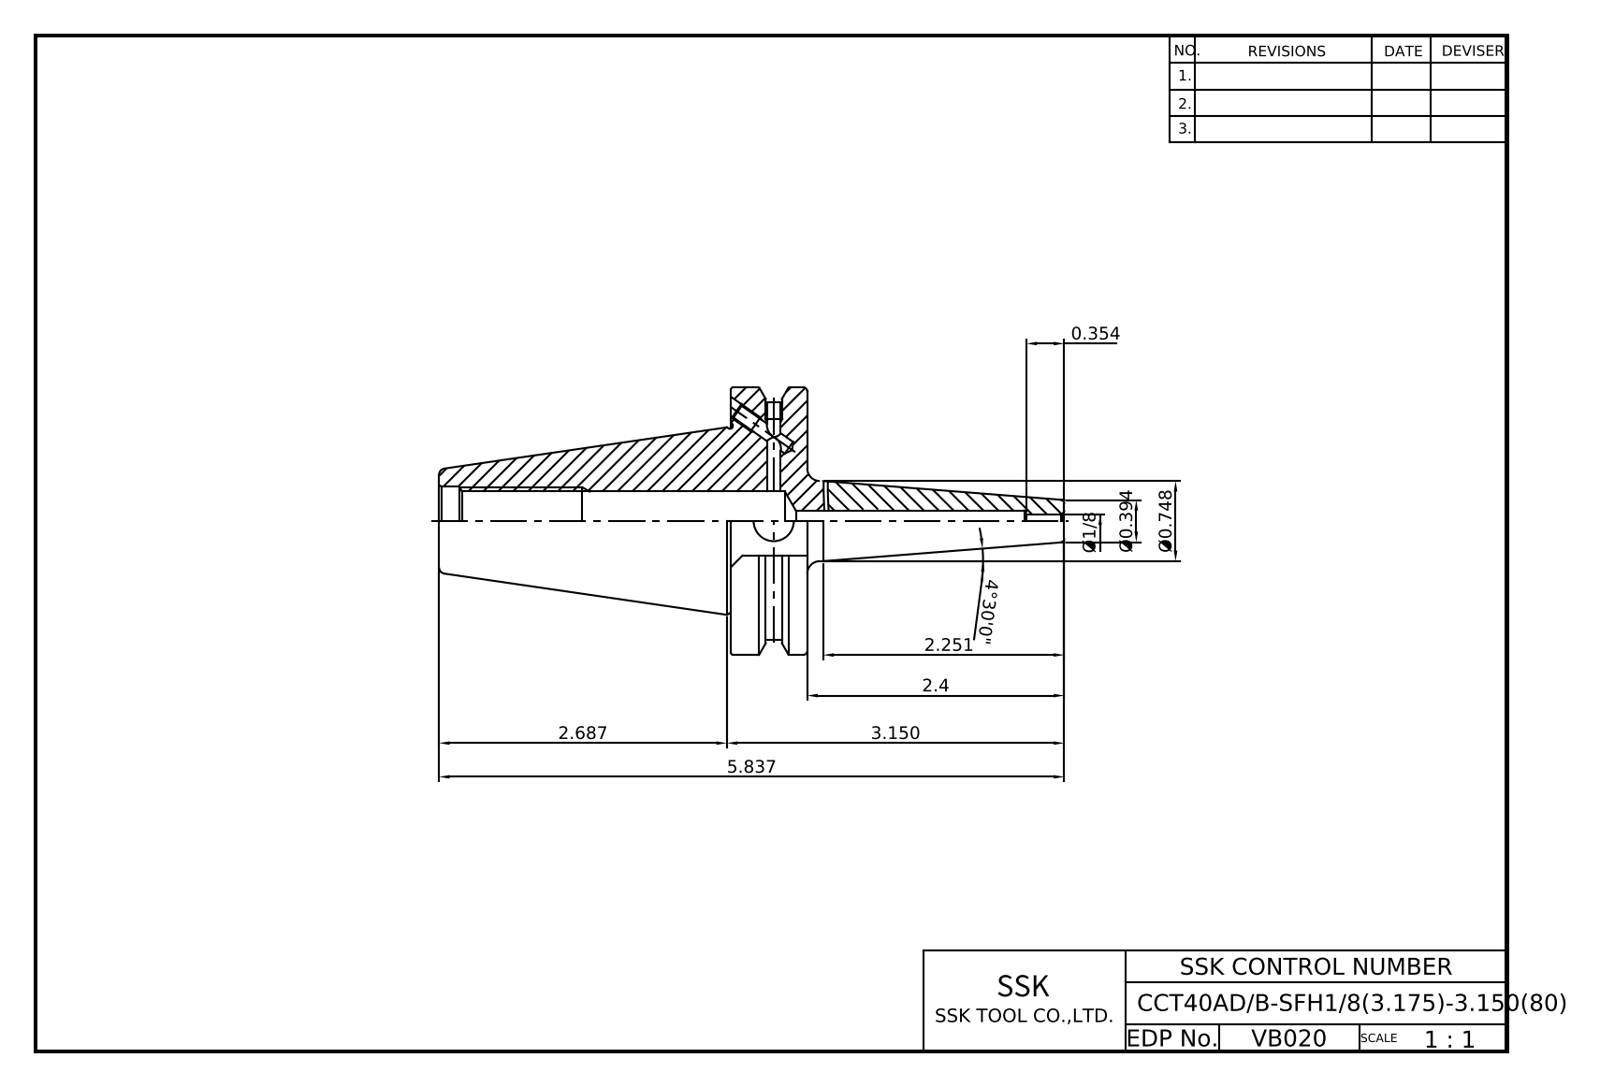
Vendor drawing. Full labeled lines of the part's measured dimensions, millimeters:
Part name (STEP PRODUCT): LO CCT40ADB-SFH3.175-3.15
STEP written by: Autodesk Inventor 2022 (AUTOMOTIVE_DESIGN)
Units: millimetres
Bodies: 1 solid, 88 faces (36 planar, 28 cylindrical, 24 other)
Overall size (bounding box): 148.25 × 63.5 × 61.09
Volume: 113 513 mm³ · Surface area: 24 719 mm²
Round holes (diameter × count): ⌀3.24 ×4, ⌀4 ×2, ⌀4.2 ×2, ⌀3.17 ×1, ⌀5 ×1, ⌀9.53 ×1, ⌀13 ×1, ⌀13.39 ×1, ⌀16.3 ×1
Round bosses / shafts (diameter × count): ⌀63.5 ×1, ⌀43.8 ×1, ⌀19 ×1
Partial cylindrical surfaces — rounded edges, fillets, slot ends (radius × count): R28.15 ×1
Main face-to-face distances: 18.05, 47.6, 16.38, 69.25, 87.3, 81.34, 12.09, 5.96, 77.51, 8.26
